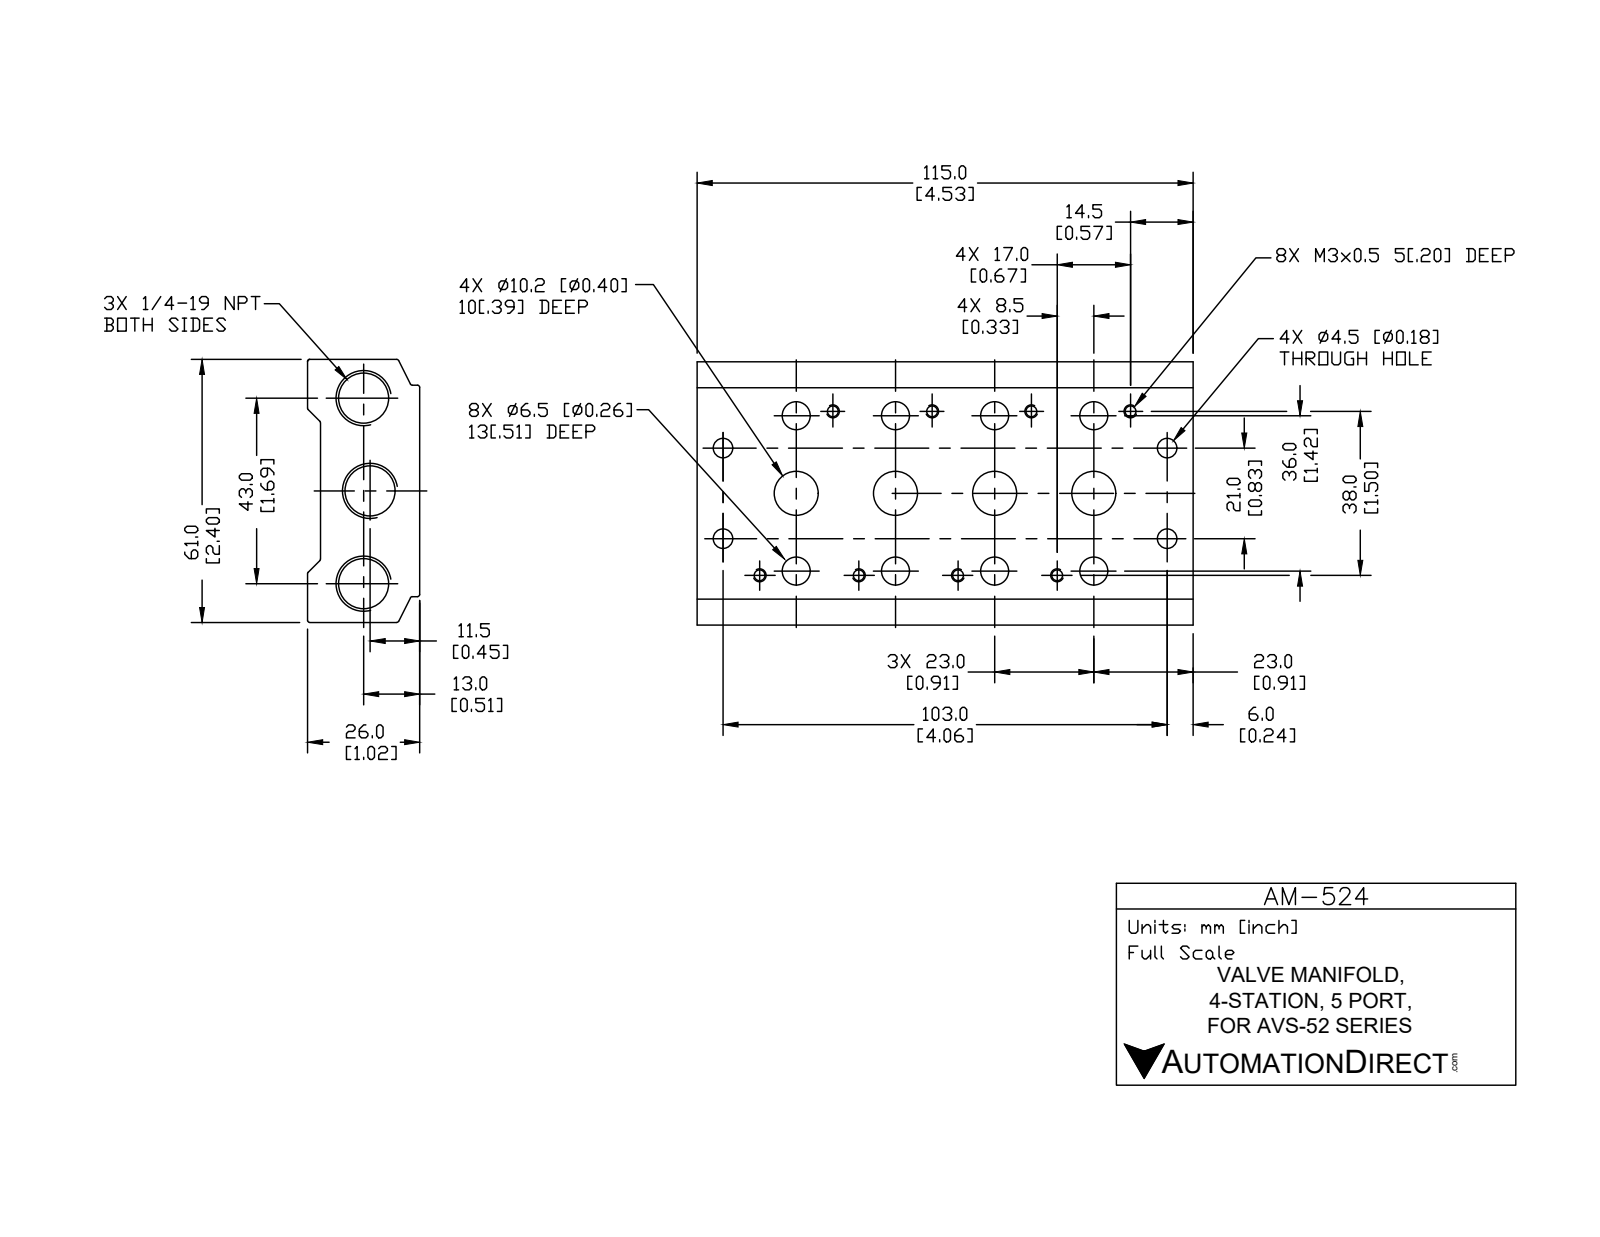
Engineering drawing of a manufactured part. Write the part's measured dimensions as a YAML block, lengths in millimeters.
part_name: "AM-524"
step_written_by: "SolidWorks 2015 (CONFIG_CONTROL_DESIGN)"
units: millimeters
bodies: {solids: 1, faces: 121, planar: 28, cylindrical: 65, other: 28}
overall_size: [115, 61, 26]
volume: 124425
surface_area: 37422
round_holes:
  - {diameter: 2.5, count: 8}
  - {diameter: 6.5, count: 8}
  - {diameter: 4.5, count: 4}
  - {diameter: 10.2, count: 4}
  - {diameter: 11.13, count: 3}
partial_cylinders:
  - {radius: 0.5, count: 11}
face_to_face_distances: [23, 61, 3, 26, 115, 6, 55, 10.02, 104.98, 49]
hole_center_spacings: [23, 29.21, 46, 8.56, 18, 20.81, 37.96, 49.4]
